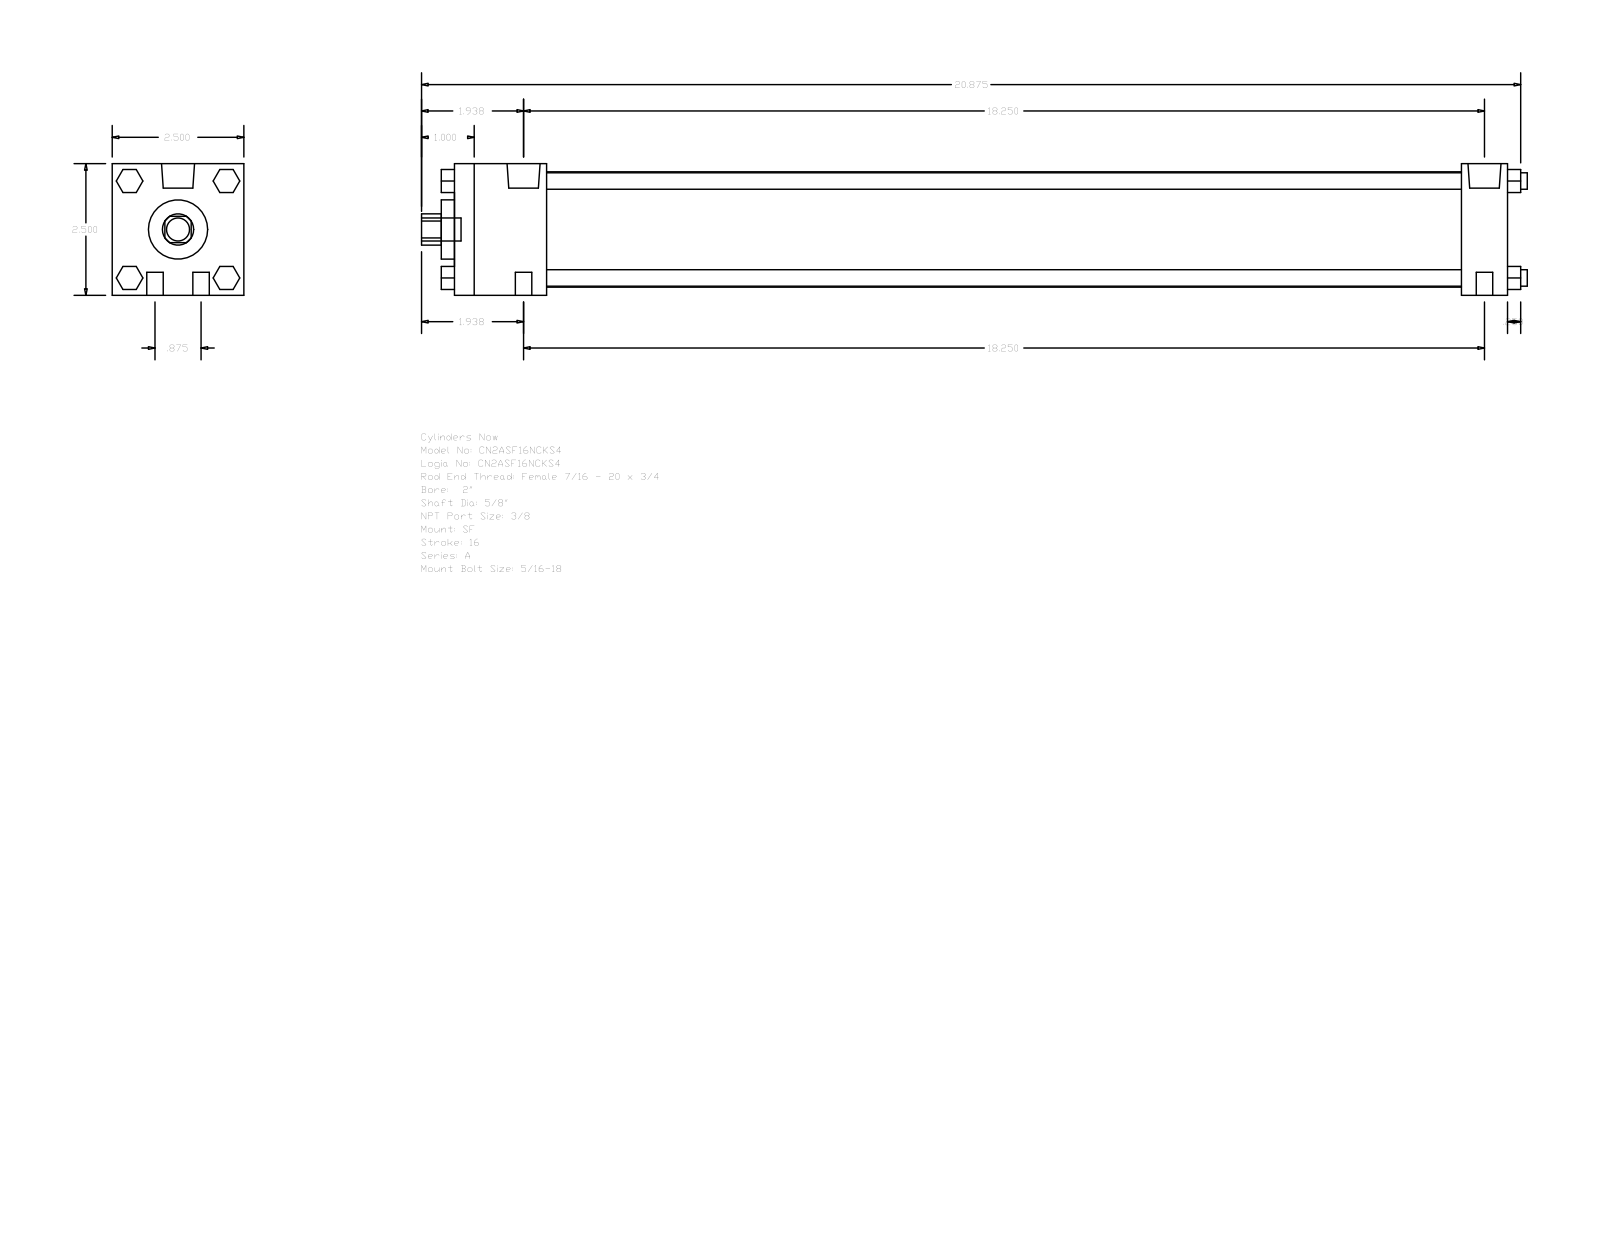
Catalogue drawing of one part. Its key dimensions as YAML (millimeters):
part_name: "A_SF__0200_0.625"
step_written_by: "GSSL Pune (CONFIG_CONTROL_DESIGN)"
units: millimeters
bodies: {solids: 0, faces: 124, planar: 94, cylindrical: 30, other: 0}
overall_size: [533.4, 63.5, 63.5]
round_holes:
  - {diameter: 15.88, count: 1}
  - {diameter: 28.57, count: 1}
  - {diameter: 55.63, count: 1}
round_bosses_or_shafts:
  - {diameter: 7.94, count: 8}
  - {diameter: 15.93, count: 2}
  - {diameter: 5.56, count: 2}
  - {diameter: 11.11, count: 1}
partial_cylinders:
  - {radius: 7.54, count: 1}
face_to_face_distances: [63.5, 508, 485.77, 22.23, 44.45, 441.32, 463.55, 514.35, 6.35, 50.8]
